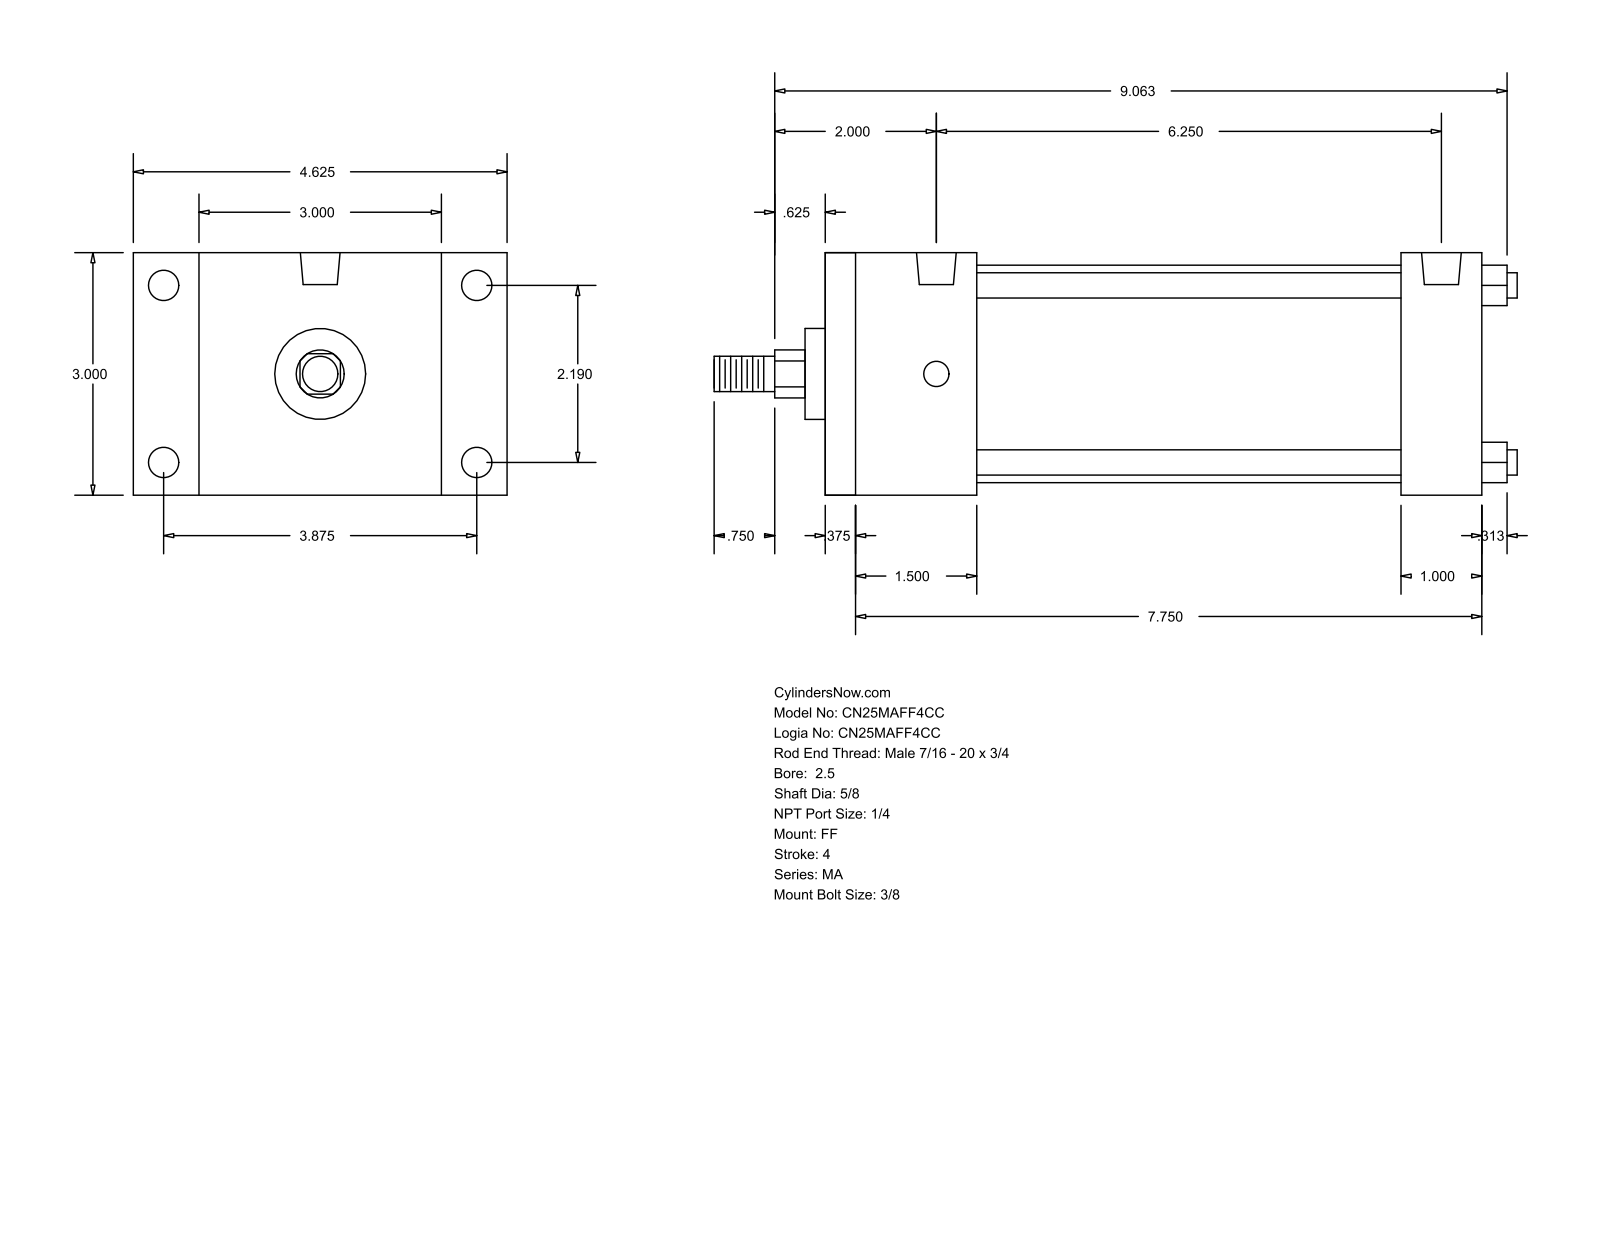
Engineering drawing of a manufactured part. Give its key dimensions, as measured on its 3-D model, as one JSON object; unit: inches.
{"part_name": "MA_FF__0250_0.625", "step_written_by": "GSSL Pune (CONFIG_CONTROL_DESIGN)", "units": "inches", "bodies": {"solids": 0, "faces": 92, "planar": 64, "cylindrical": 28, "other": 0}, "overall_size": [9.937, 4.625, 3], "round_holes": [[0.313, 4], [0.375, 4], [0.492, 2]], "round_bosses_or_shafts": [[0.313, 4], [2.69, 1], [1.125, 1], [0.625, 1], [0.437, 1]], "partial_cylinders_radius": [[0.297, 1]], "face_to_face_distances": [3, 8.125, 7.75, 0.375, 1, 1.875, 7.125, 1.5, 6.75, 5.25], "hole_center_spacings": [2.19, 3.875, 4.451, 6.25]}
